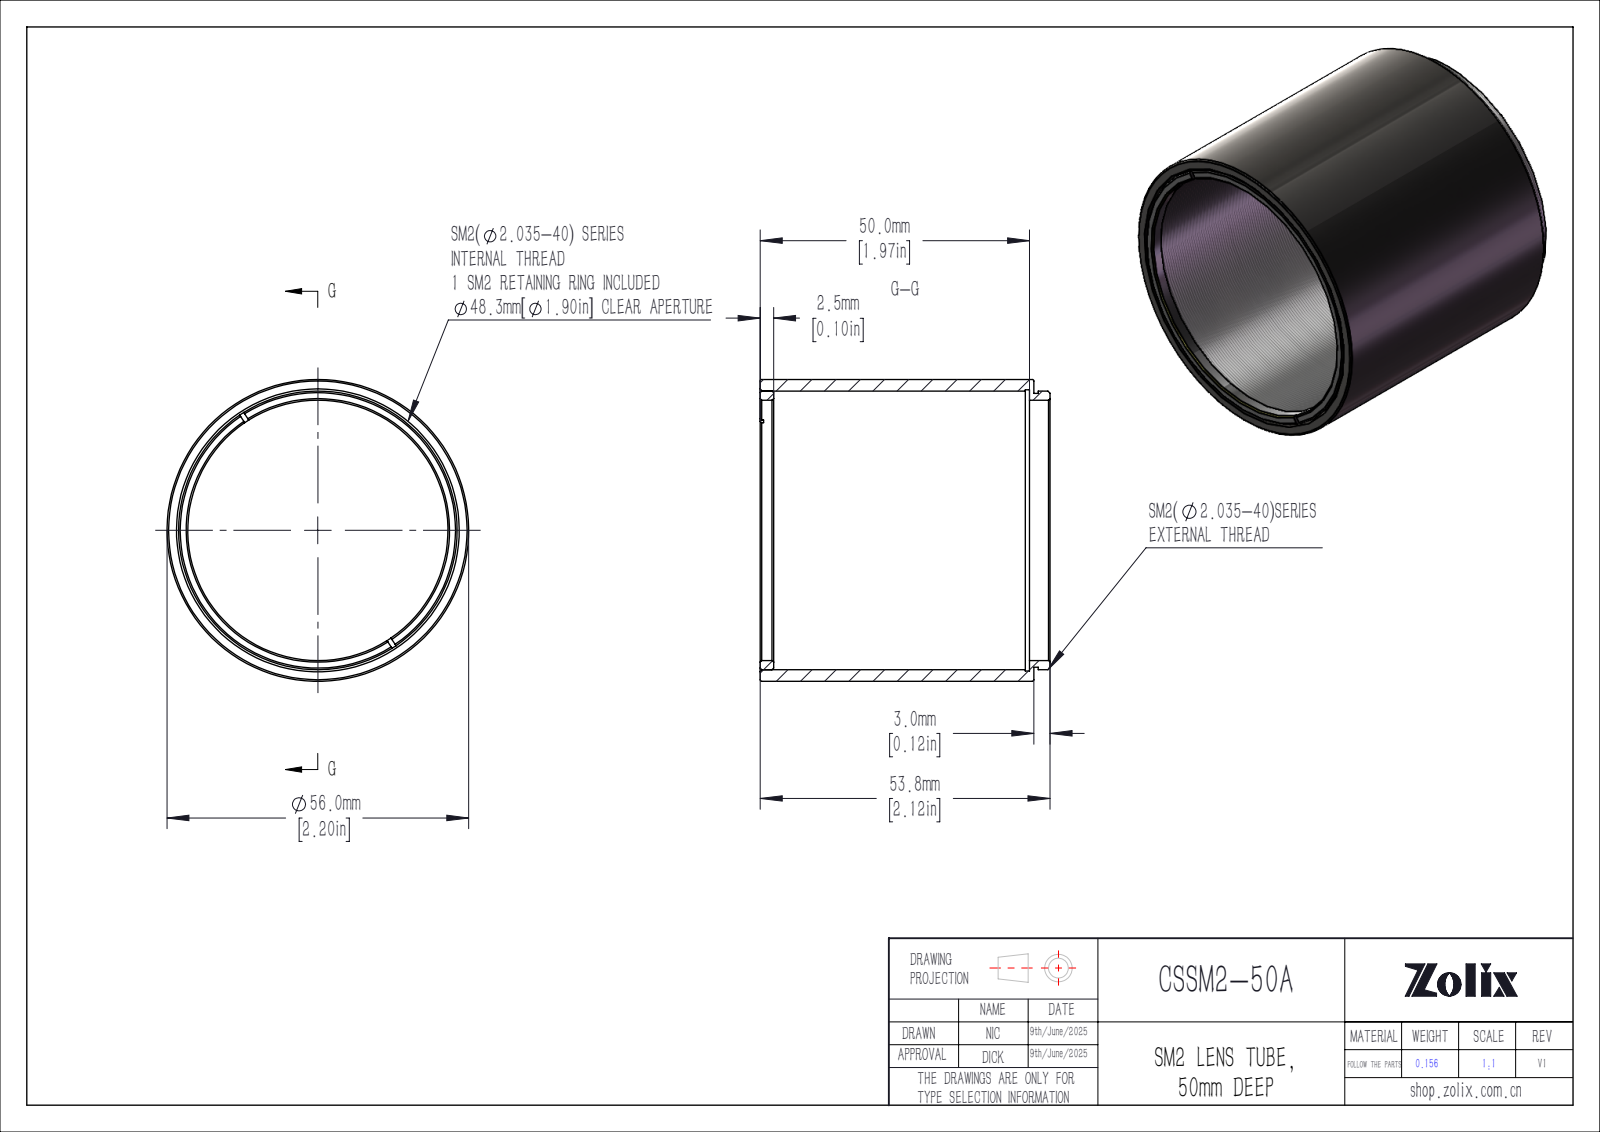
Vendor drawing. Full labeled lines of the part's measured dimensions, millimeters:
Part name (STEP PRODUCT): CSSM2-50A
STEP written by: SolidWorks 2020 (CONFIG_CONTROL_DESIGN)
Units: millimetres
Bodies: 2 solids, 351 faces (56 planar, 37 cylindrical, 258 other)
Overall size (bounding box): 56 × 56 × 53.8
Volume: 20 039 mm³ · Surface area: 20 679 mm²
Round holes (diameter × count): ⌀48.3 ×1, ⌀52.2 ×1
Round bosses / shafts (diameter × count): ⌀56 ×1, ⌀51.69 ×1, ⌀50.8 ×1
Partial cylindrical surfaces — rounded edges, fillets, slot ends (radius × count): R27.98 ×1
Main face-to-face distances: 0.8, 50.8, 50, 2.5, 47.5, 48.3, 53.8, 51.3, 3.8, 3
